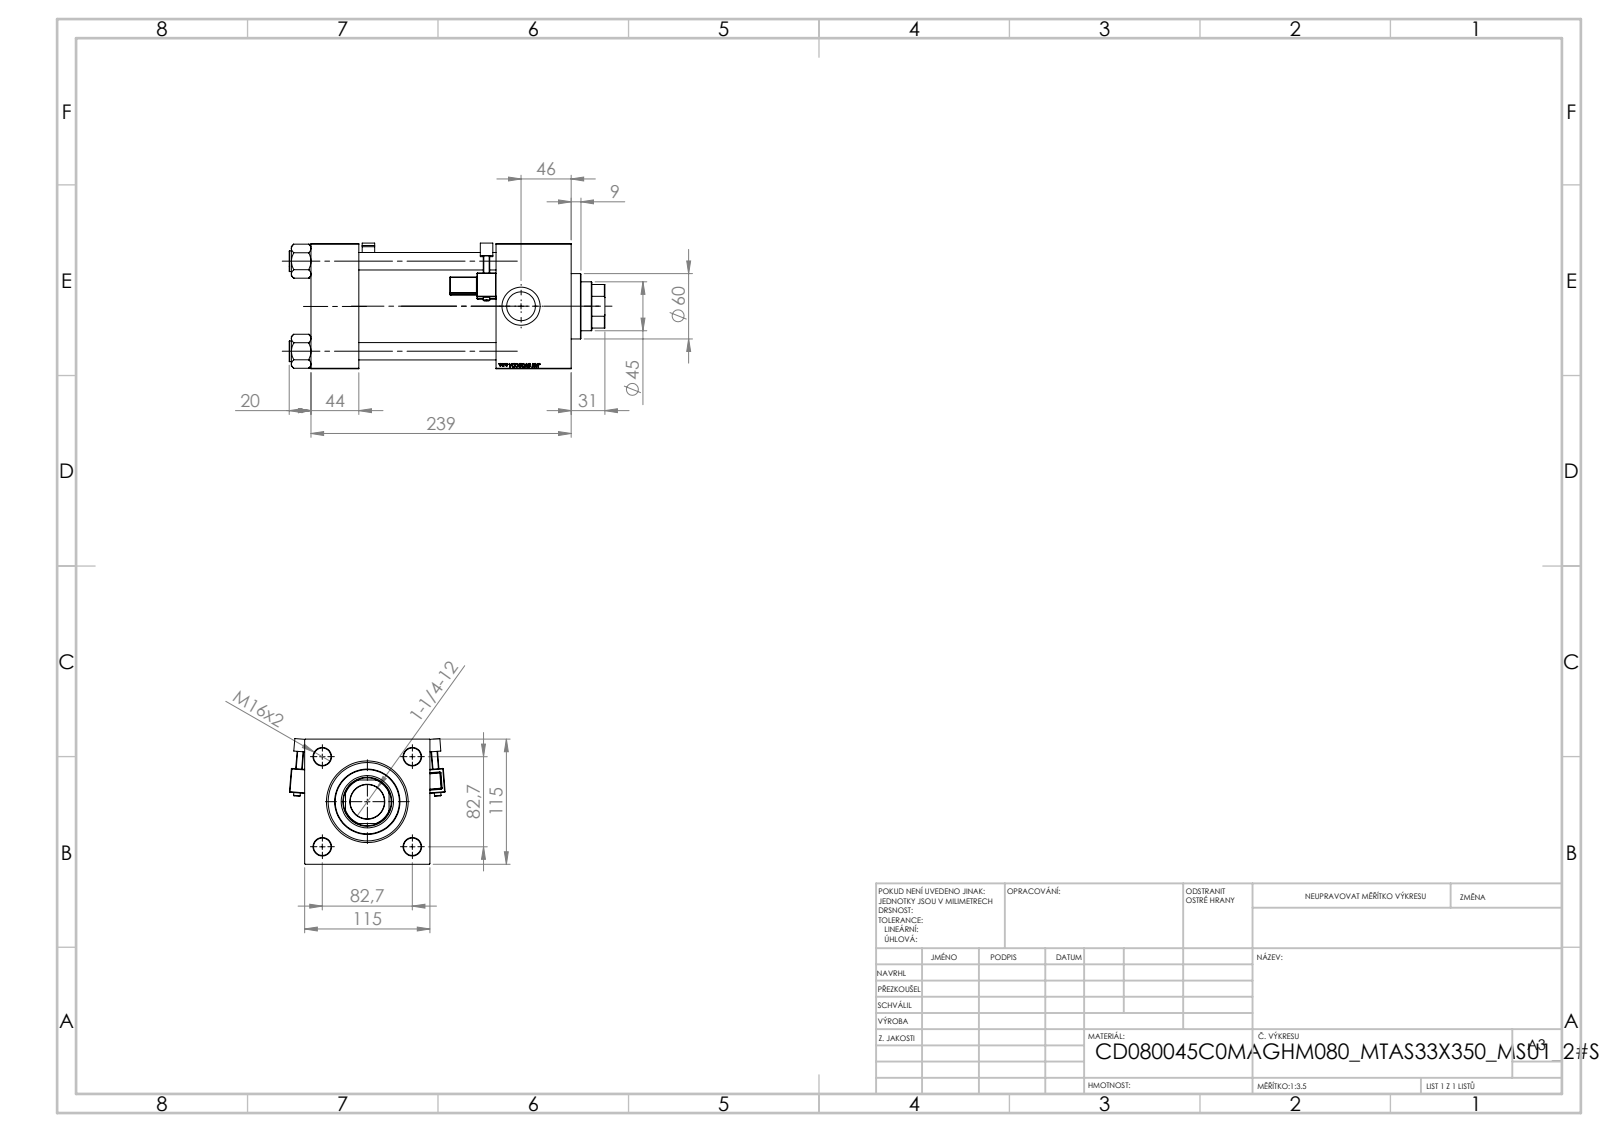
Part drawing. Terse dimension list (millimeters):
name: NUT_M5_V215CD_C; V215CD_C_TYCINKA; V215CR_MSU; V215CD_VCP_C (+2 more)
written by: SolidWorks 2019 (CONFIG_CONTROL_DESIGN)
unit: mm
bodies: 13 solids, 1351 faces (632 planar, 147 cylindrical, 572 other)
size: 290 × 142.94 × 115.49
volume: 2 051 000 mm³; area: 338 173 mm²
holes: 4× ⌀16, 2× ⌀7, 2× ⌀26.44, 2× ⌀35, 1× ⌀31.5, 1× ⌀45, 1× ⌀48, 1× ⌀61, 1× ⌀72, 1× ⌀80
bosses: 4× ⌀19, 2× ⌀6, 1× ⌀86, 1× ⌀60
rounds: 48× R0.5, 2× R1, 2× R2.5, 2× R4, 1× R22
face distances: 115, 44, 69, 239, 195, 170, 126, 46, 210.3, 166.3
hole spacings: 58.48, 82.7, 116.96
